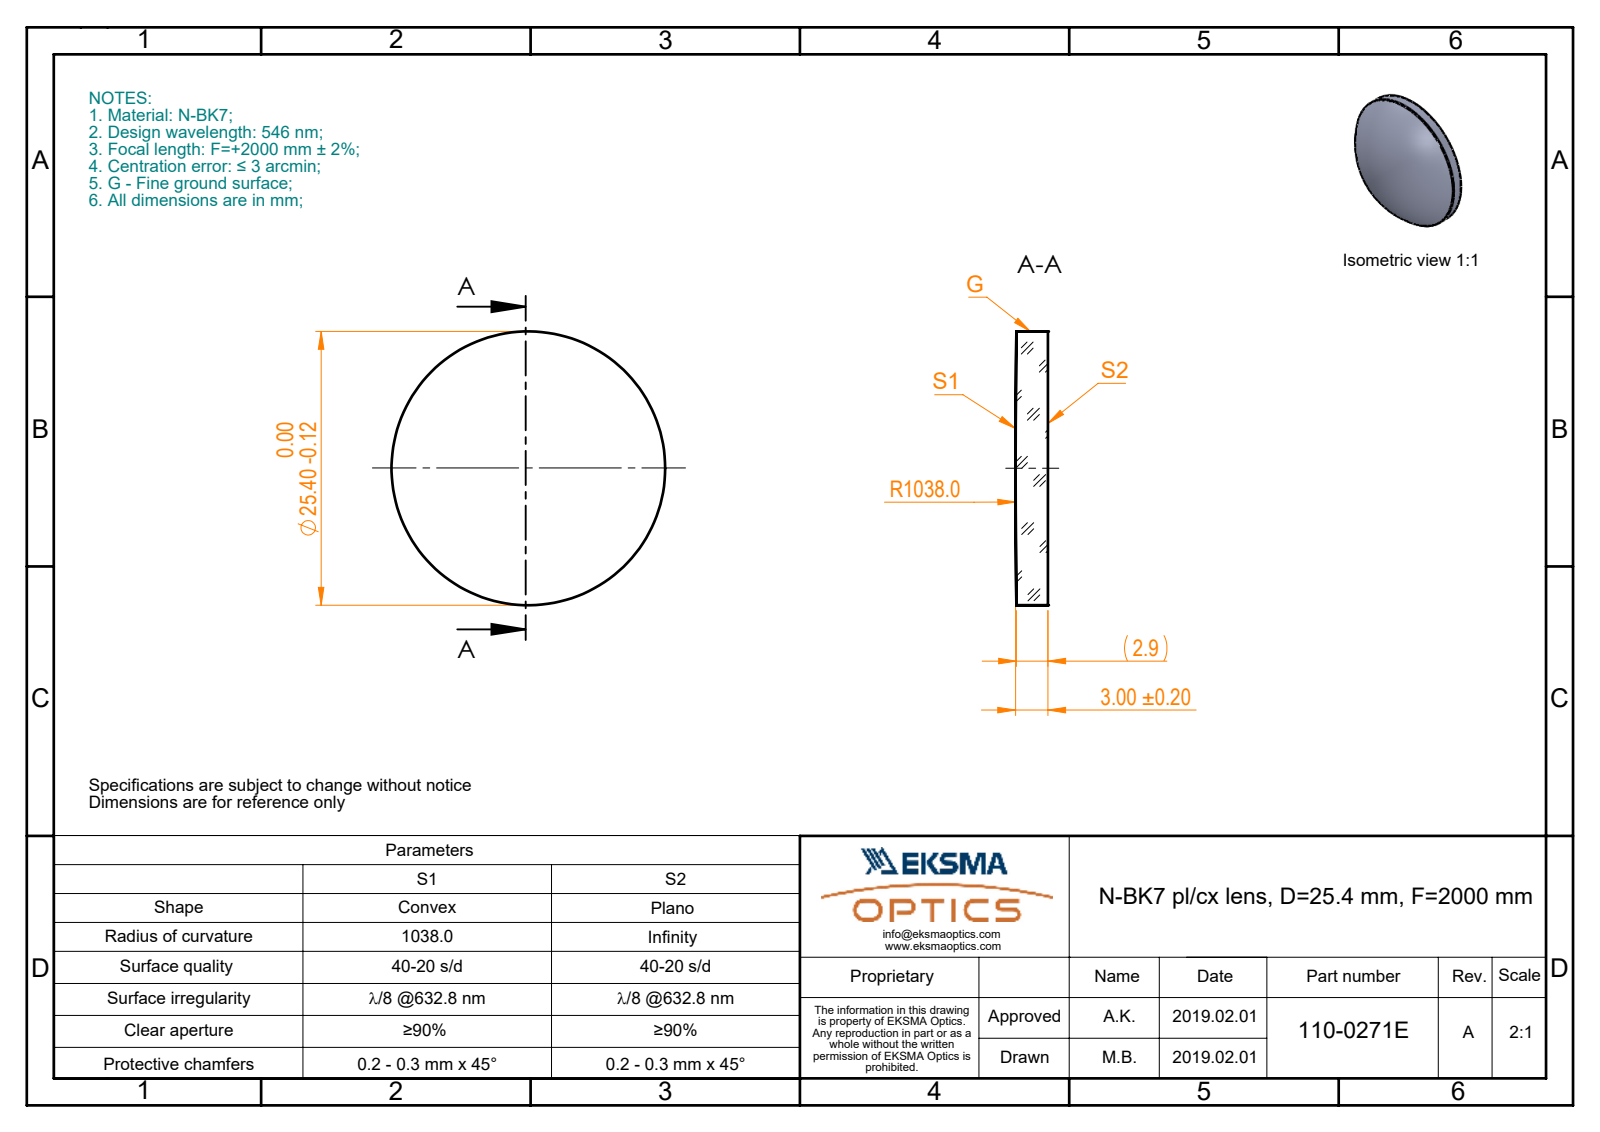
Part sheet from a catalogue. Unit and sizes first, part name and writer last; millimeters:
Units: millimetres
Overall size (bounding box): 25.4 × 25.4 × 3
Round bosses / shafts (diameter × count): ⌀25.4 ×1
Volume: 1 500 mm³ · Surface area: 1 247 mm²
Bodies: 1 solid, 5 faces (1 planar, 2 cylindrical, 2 other)
Part name (STEP PRODUCT): 110-0271E BK7 pl-cx 25.4 F2000
STEP written by: SolidWorks 2017 (CONFIG_CONTROL_DESIGN)
